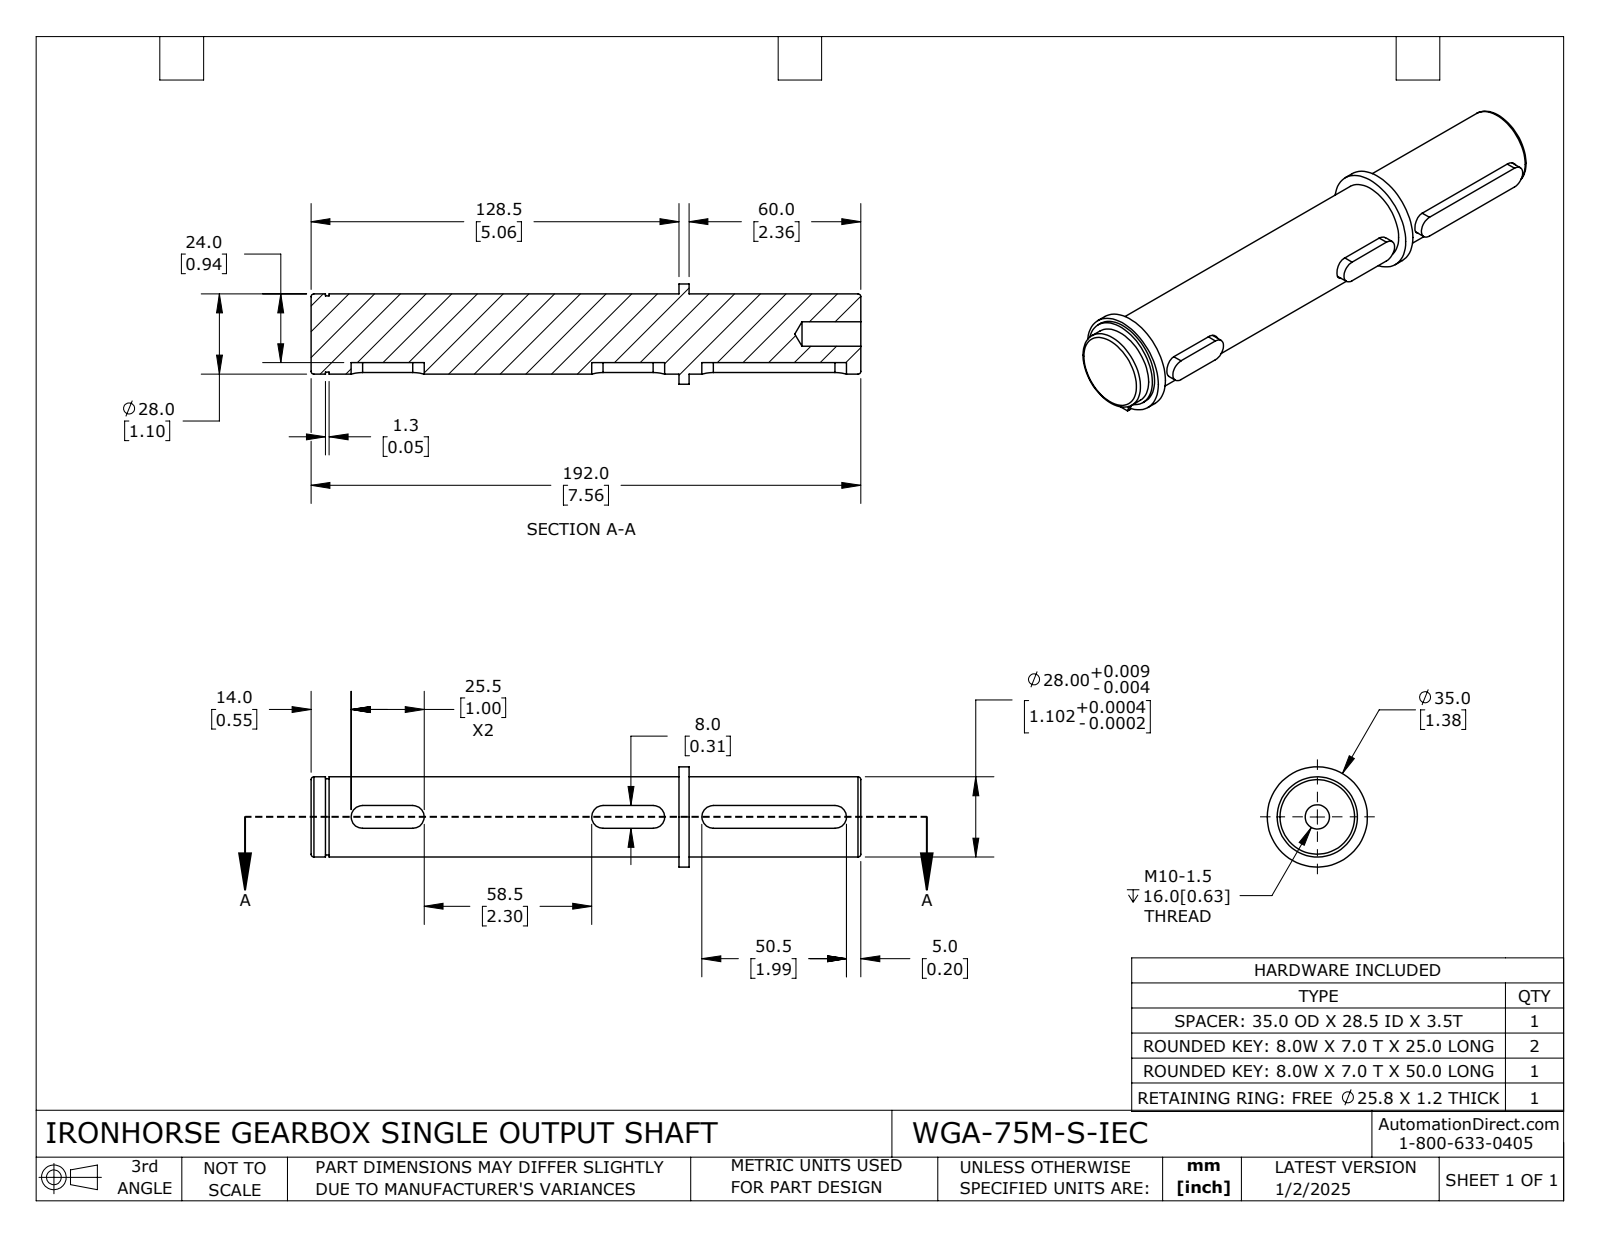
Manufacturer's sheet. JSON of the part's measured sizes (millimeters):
{"part_name": "WGA-75M-S-IEC", "step_written_by": "SolidWorks 2024 (CONFIG_CONTROL_DESIGN)", "units": "millimeters", "bodies": {"solids": 6, "faces": 91, "planar": 37, "cylindrical": 48, "other": 6}, "overall_size": [192, 35.3, 35], "volume_mm3": 121891, "surface_area_mm2": 25459, "round_holes": [[1.9, 2], [8.5, 1], [26.4, 1], [28.5, 1]], "round_bosses_or_shafts": [[35, 1], [31.35, 1], [28, 1], [26.6, 1]], "partial_cylinders_radius": [[4, 10], [0.5, 2], [2.8, 2]], "face_to_face_distances": [8, 7, 3.5, 122.2, 6.3, 192, 185.7, 132, 125.7, 60], "hole_center_spacings": [15.9, 3.05]}
